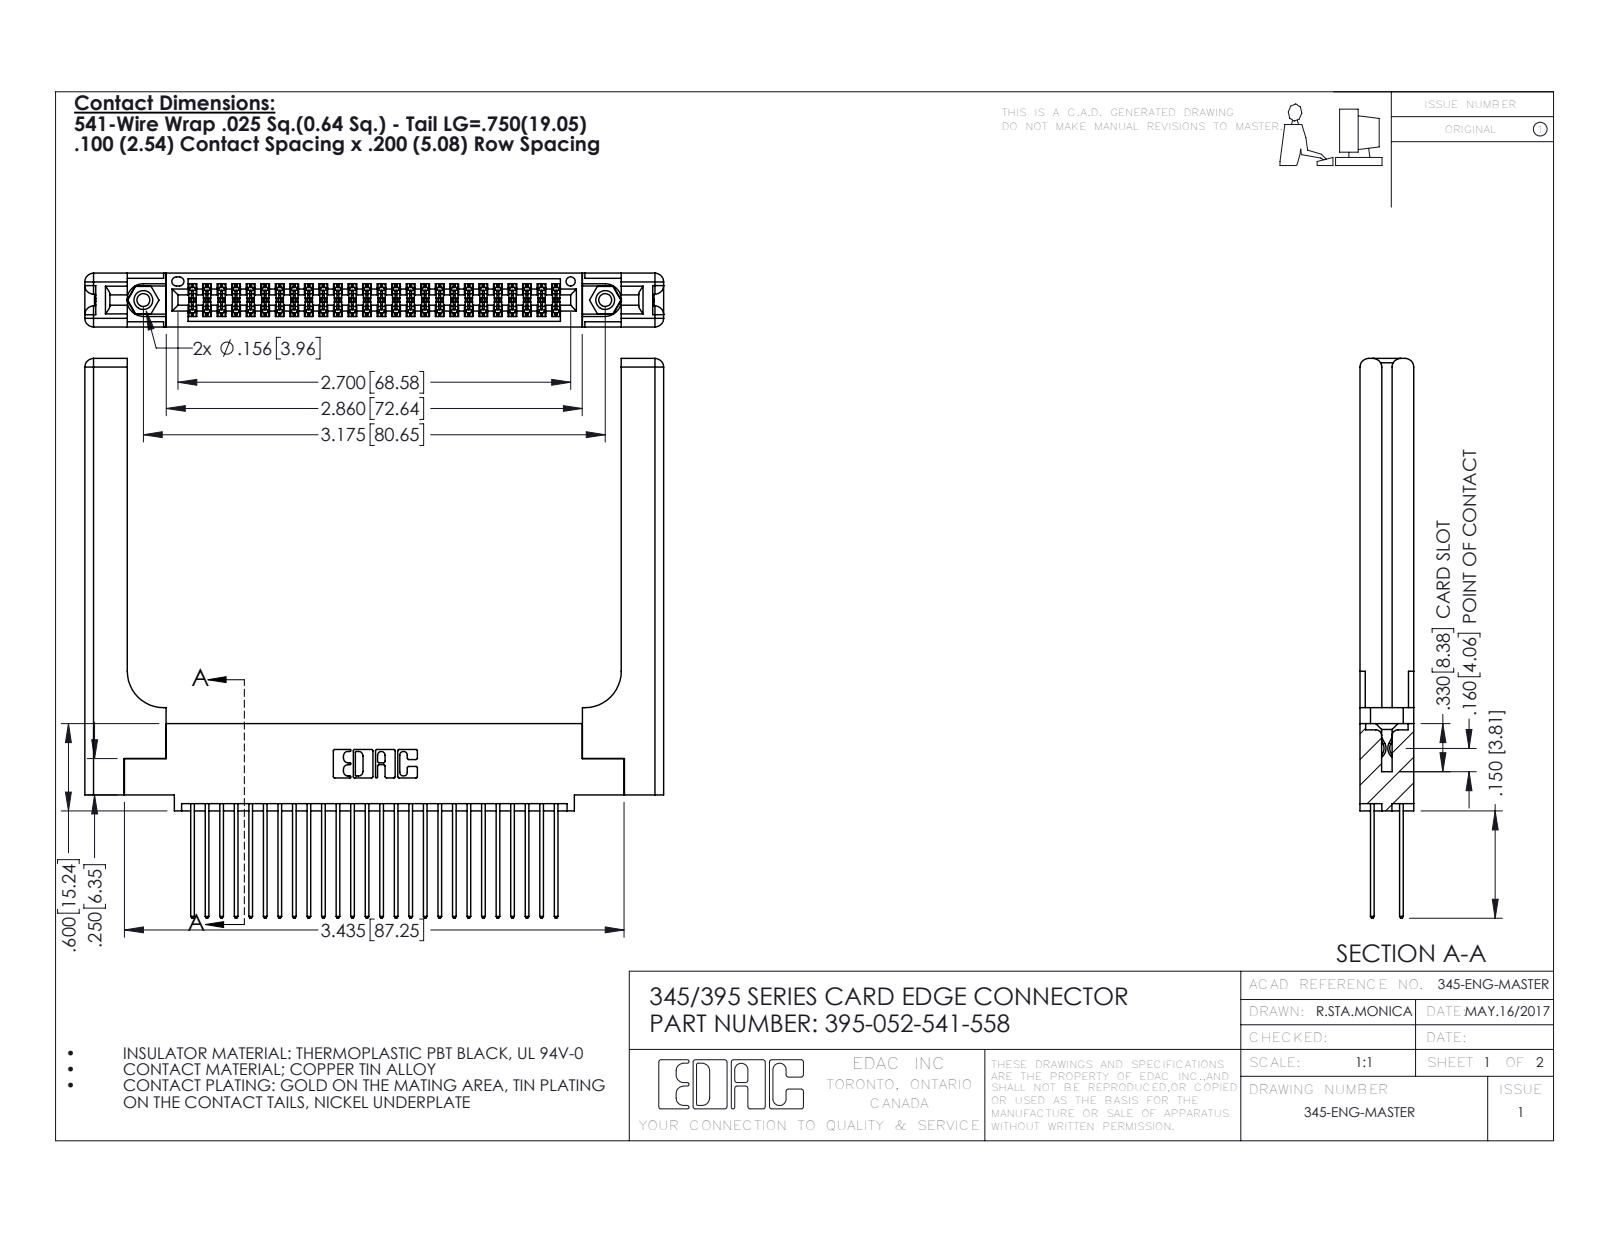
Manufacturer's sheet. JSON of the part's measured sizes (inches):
{"part_name": "345-220-058_345-220-058; 345-250-001_345-250-001-102; 345 Part_0.110 Offset - 0.156 Dia-TH; 345-292-001_345-293-141 (+1 more)", "step_written_by": "SolidWorks 2016 (CONFIG_CONTROL_DESIGN)", "units": "inches", "bodies": {"solids": 57, "faces": 2986, "planar": 1948, "cylindrical": 978, "other": 60}, "overall_size": [3.979, 3.847, 0.37], "volume_in3": 1.121, "surface_area_in2": 32.35, "round_holes": [[0.089, 2], [0.125, 2], [0.156, 2], [0.064, 1]], "round_bosses_or_shafts": [[0.155, 2]], "partial_cylinders_radius": [[0.006, 78], [0.01, 52], [0.01, 22], [0.06, 16], [0.007, 6], [0.031, 6], [0.026, 3], [0.014, 2]], "face_to_face_distances": [0.072, 0.298, 0.37, 0.098, 0.272, 0.025, 0.2, 0.225, 0.148, 0.15], "hole_center_spacings": [0.27, 2.94, 3.175]}
